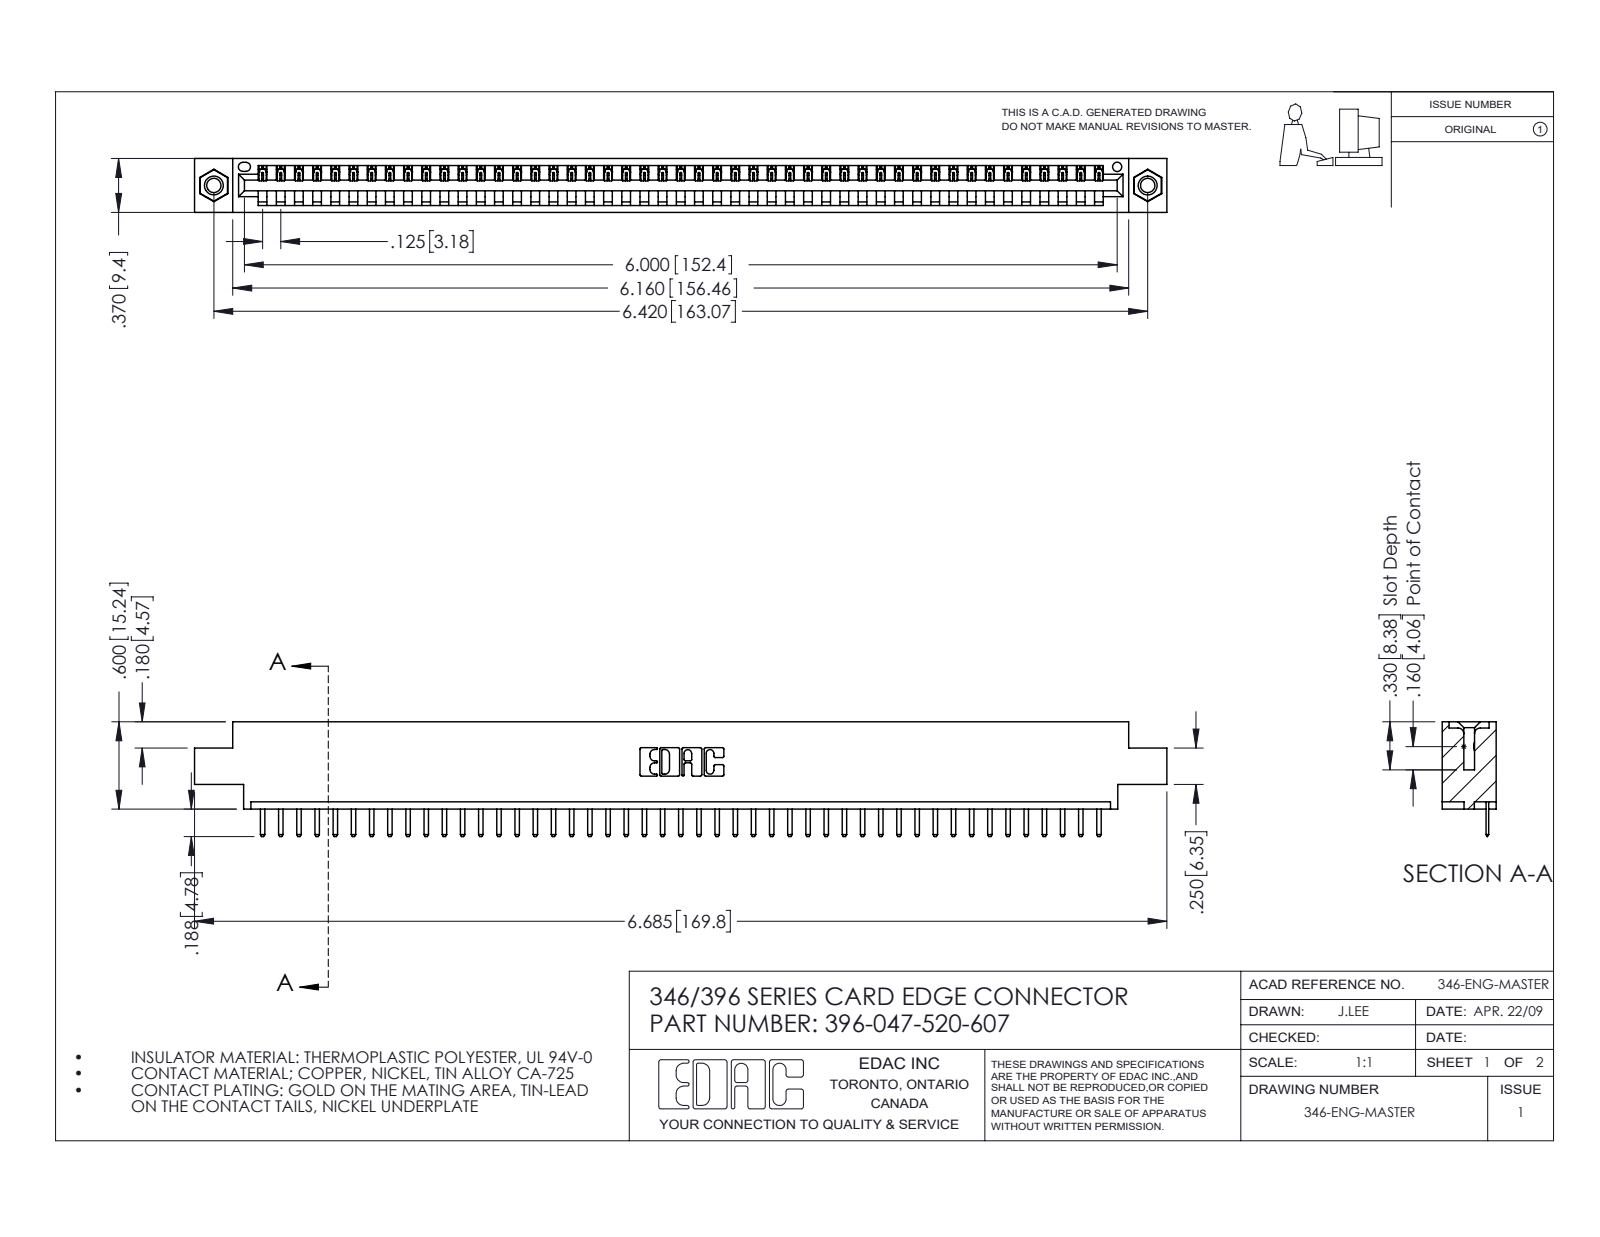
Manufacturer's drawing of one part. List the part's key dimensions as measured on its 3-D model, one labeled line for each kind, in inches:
Part name (STEP PRODUCT): 345-250-001_345-250-005-103; 396-047-520-607; 345-292-001_345-293-120; 346 Part_0.170 Offset - 0.156 Dia-TI
STEP written by: SolidWorks 2016 (CONFIG_CONTROL_DESIGN)
Units: inches
Bodies: 50 solids, 3100 faces (2086 planar, 998 cylindrical, 16 other)
Overall size (bounding box): 6.685 × 0.788 × 0.37
Volume: 0.975 in³ · Surface area: 30.65 in²
Round holes (diameter × count): ⌀0.098 ×2, ⌀0.125 ×2, ⌀0.156 ×2, ⌀0.064 ×1
Round bosses / shafts (diameter × count): ⌀0.155 ×2
Partial cylindrical surfaces — rounded edges, fillets, slot ends (radius × count): R0.01 ×96, R0.006 ×94, R0.01 ×22, R0.007 ×6, R0.031 ×6, R0.026 ×3, R0.031 ×2, R0.04 ×2
Main face-to-face distances: 0.048, 0.322, 0.37, 0.25, 0.222, 0.148, 0.1, 0.174, 0.072, 0.298
Hole centre spacings: 0.246, 6.211, 6.42
